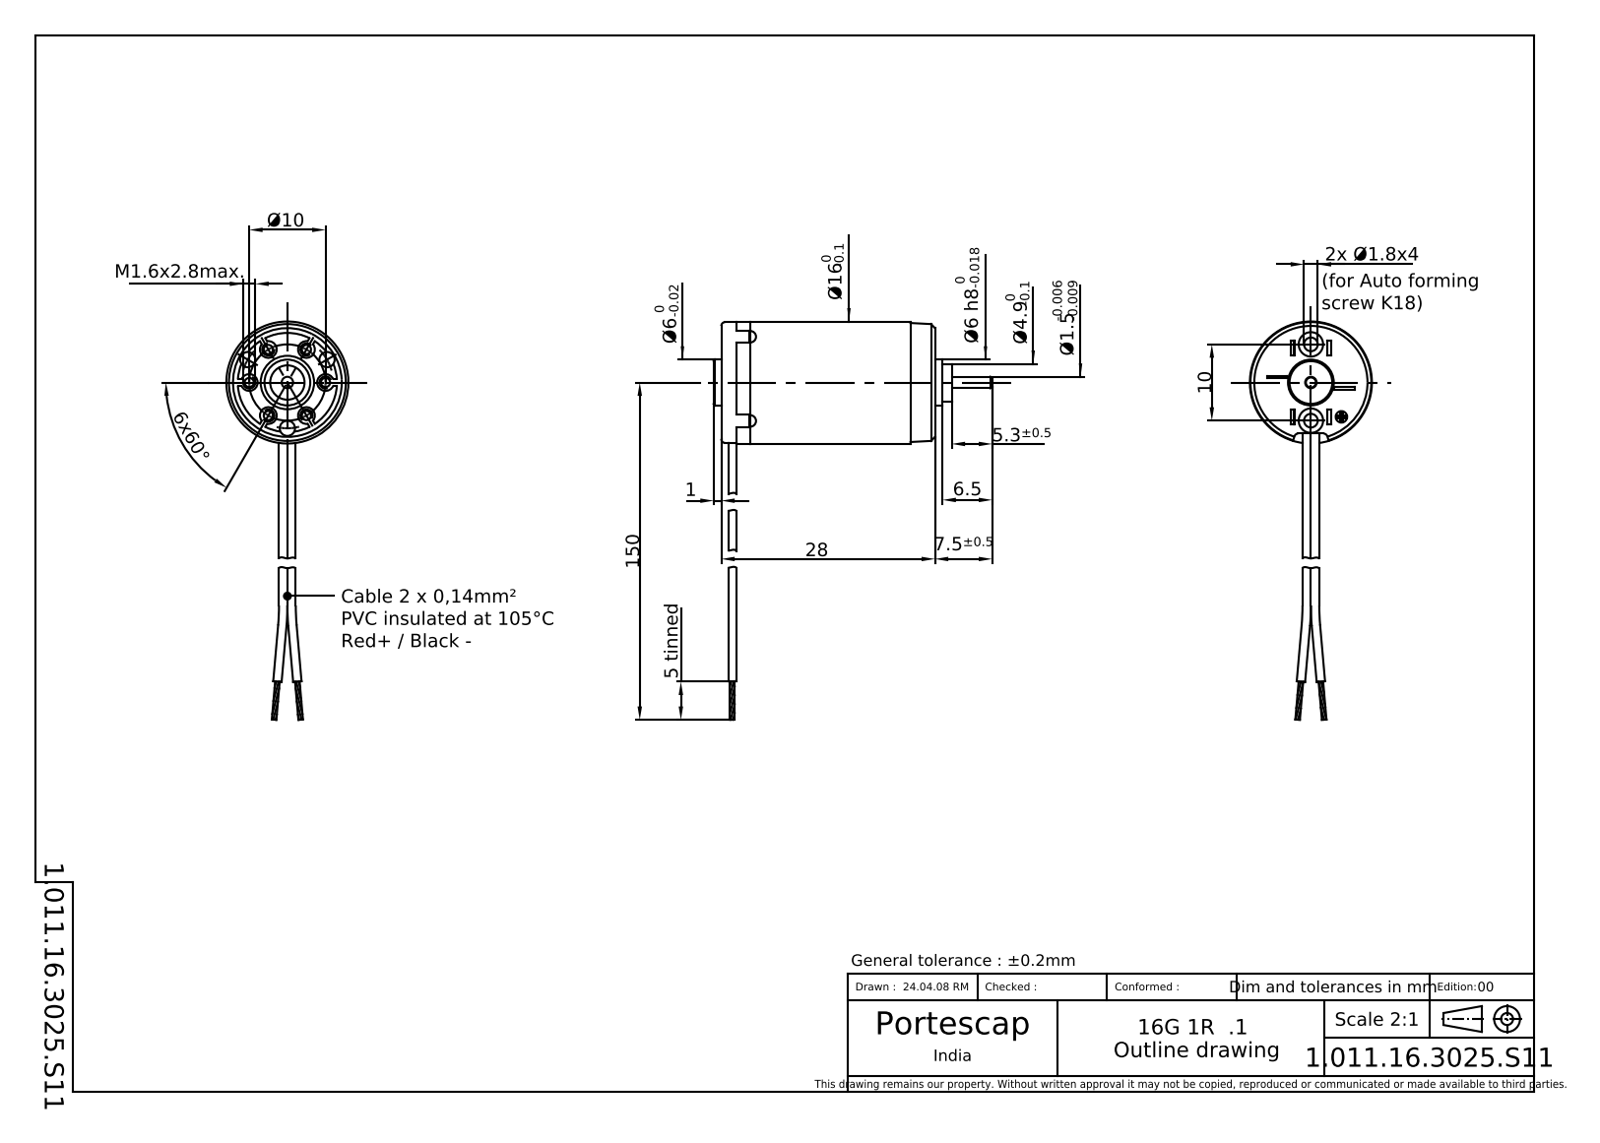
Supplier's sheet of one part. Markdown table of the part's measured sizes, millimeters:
| quantity | value |
| --- | --- |
| part name | 16G88_208E_1 |
| STEP written by | PRO/ENGINEER BY PARAMETRIC TECHNOLOGY CORPORATION, 2014310 (CONFIG_CONTROL_DESIGN) |
| units | millimeters |
| bodies | 1 solid, 213 faces (91 planar, 57 cylindrical, 65 other) |
| overall size | 158 × 36.5 × 16 |
| volume | 5 777 mm³ |
| surface area | 3 084 mm² |
| round holes (diameter × count) | 1.25 × 6, 1.8 × 2, 1.5 × 1 |
| round bosses / shafts (diameter × count) | 2.2 × 6, 2 × 3, 1.1 × 2, 0.5 × 2, 16 × 1, 15.84 × 1, 6 × 1, 4.5 × 1 |
| partial cylindrical surfaces (radius × count) | 0.5 × 2, 0.55 × 2 |
| main face-to-face distances | 28, 2, 1.5, 29, 1, 0.5, 27.5, 27, 26, 28.5 |
| hole center spacings | 5, 8.66, 2.59, 7.07, 9.66, 10, 1.51, 4.03 |
